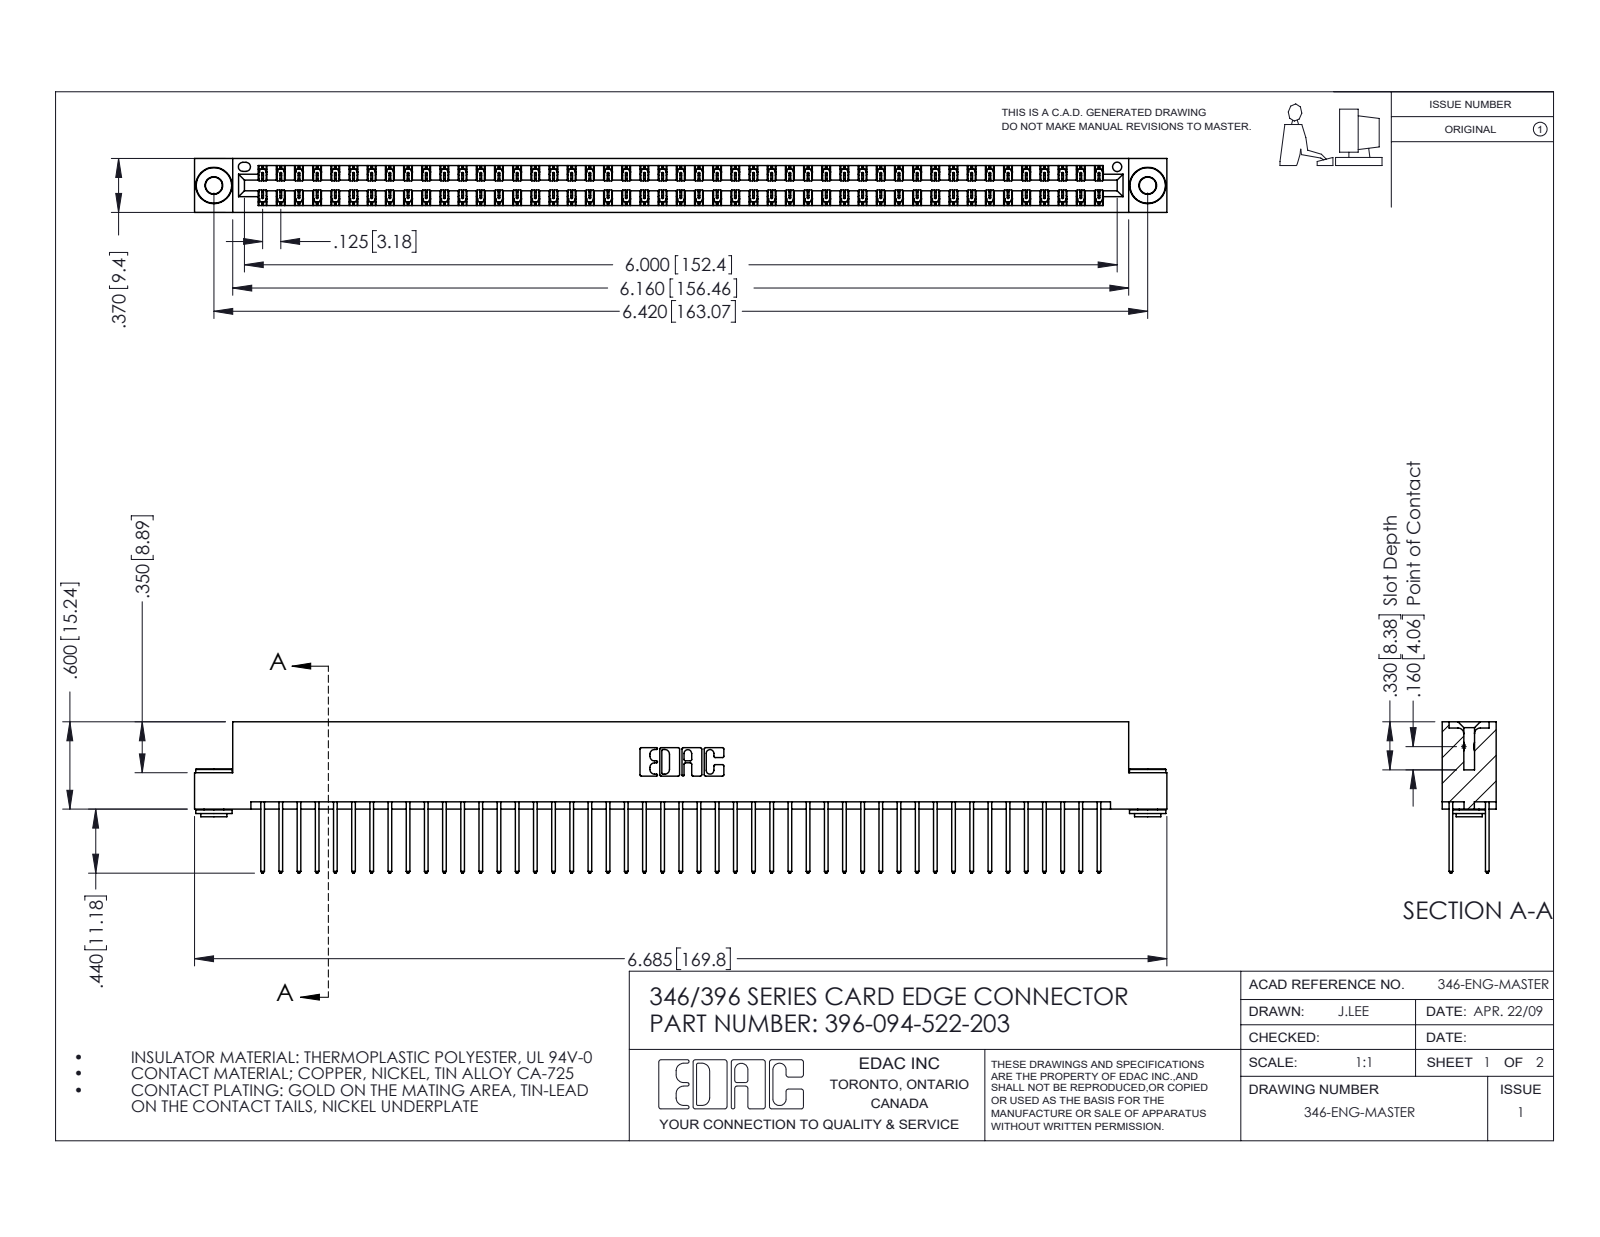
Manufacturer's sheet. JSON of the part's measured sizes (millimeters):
{"part_name": "345-250-002_345-250-002-102; 345-292-001_345-293-122; 346 Part_Flush Mounting Lugs - 0.156 Dia-TH; 396-094-522-203", "step_written_by": "SolidWorks 2016 (CONFIG_CONTROL_DESIGN)", "units": "millimeters", "bodies": {"solids": 97, "faces": 5048, "planar": 3376, "cylindrical": 1664, "other": 8}, "overall_size": [169.8, 26.4, 9.4], "volume_mm3": 16860, "surface_area_mm2": 24580, "round_holes": [[2.9, 2], [4, 2], [1.6, 1]], "round_bosses_or_shafts": [[6.4, 2], [4.6, 2], [3.5, 2]], "partial_cylinders_radius": [[0.2, 141], [0.3, 94], [0.3, 22], [0.2, 6], [0.8, 6], [0.7, 3], [0.4, 2], [0.6, 2]], "face_to_face_distances": [1.2, 8.2, 6.4, 0.6, 9.4, 1.8, 7.6, 7, 3.8, 5.6], "hole_center_spacings": [6.2, 157.8, 163.1]}
